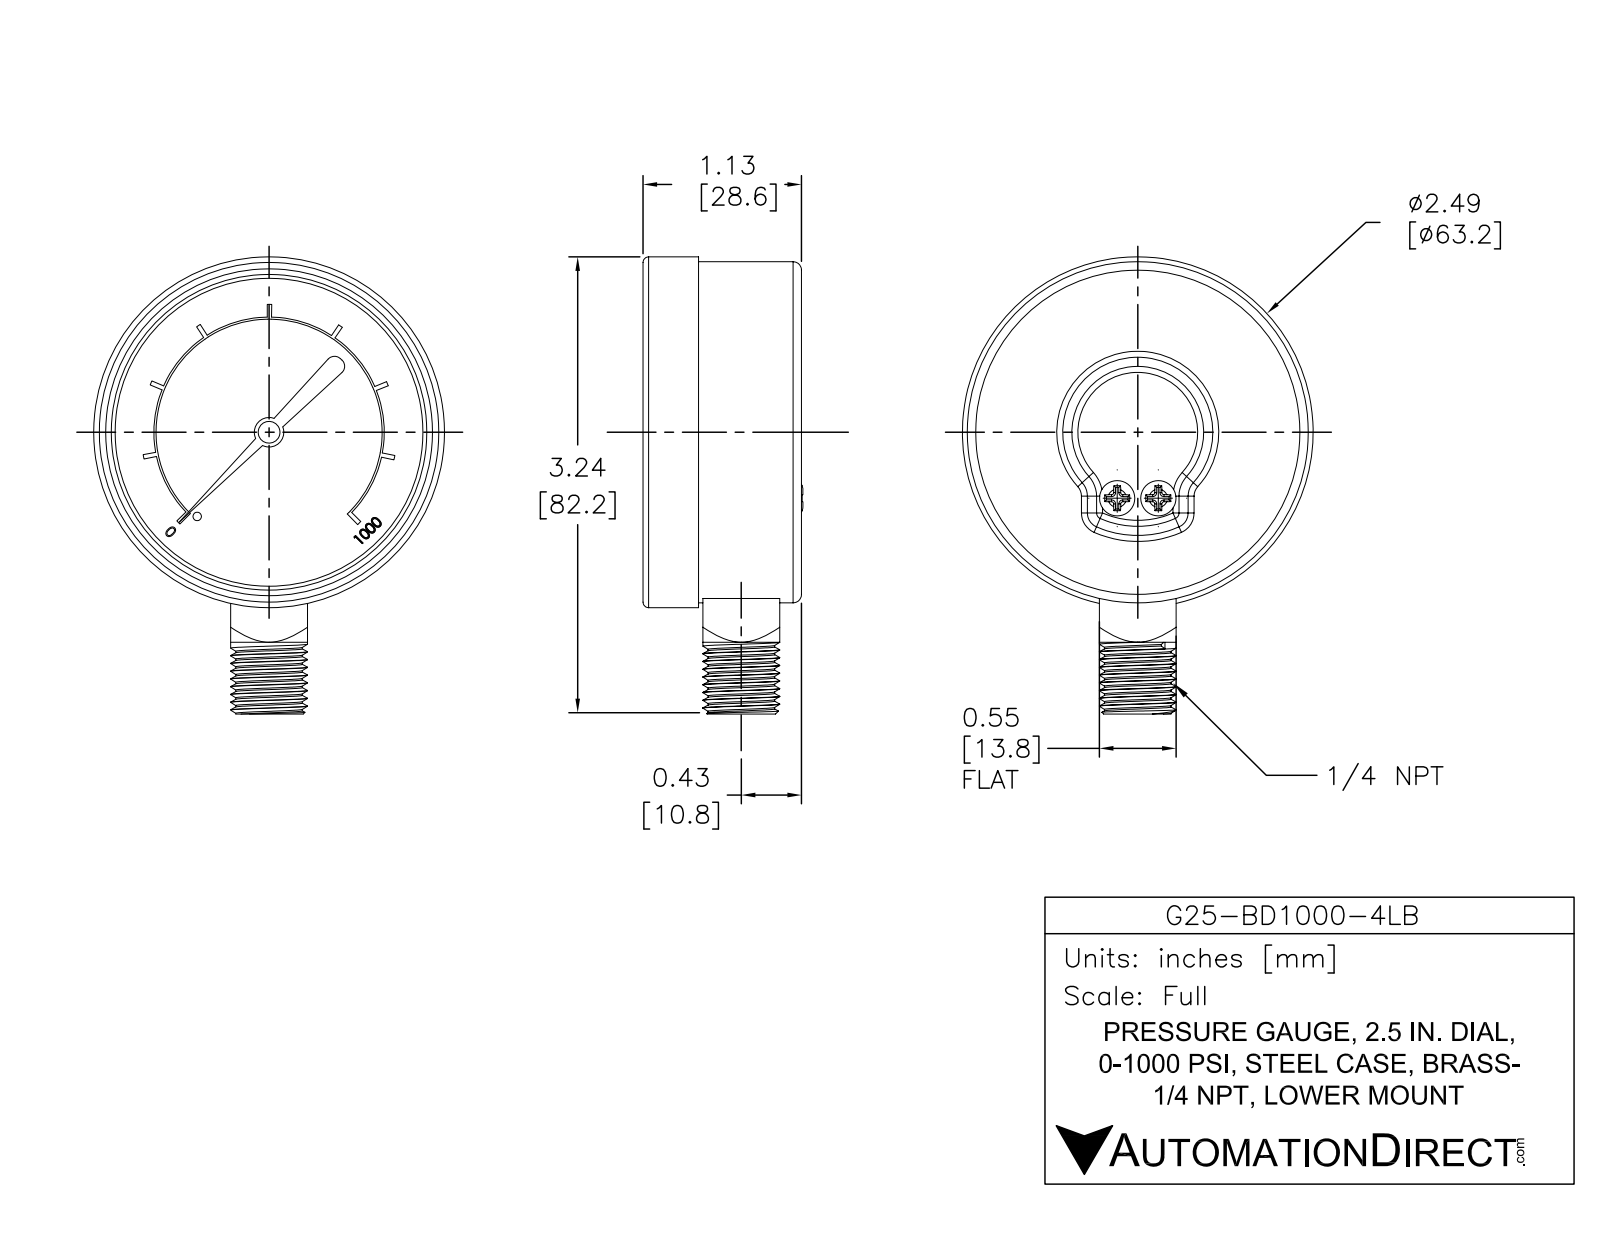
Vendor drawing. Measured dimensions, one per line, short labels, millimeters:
name: G25-BD1000-4LB
written by: SolidWorks 2021 (AUTOMOTIVE_DESIGN)
unit: mm
bodies: 1 solid, 225 faces (117 planar, 35 cylindrical, 73 other)
size: 82.4 × 63.2 × 28.8
volume: 70 270 mm³; area: 14 450 mm²
holes: 1× ⌀3.6, 1× ⌀55.5
bosses: 2× ⌀6.4, 1× ⌀63.2, 1× ⌀61.5, 1× ⌀13.8, 1× ⌀3.9, 1× ⌀3.1, 1× ⌀1.5
rounds: 6× R1.5, 1× R2.7, 1× R20.4, 1× R20.8
face distances: 21.2, 2.5, 18.7, 28.6, 26, 7.4, 13.8, 18.6, 16, 2.6
